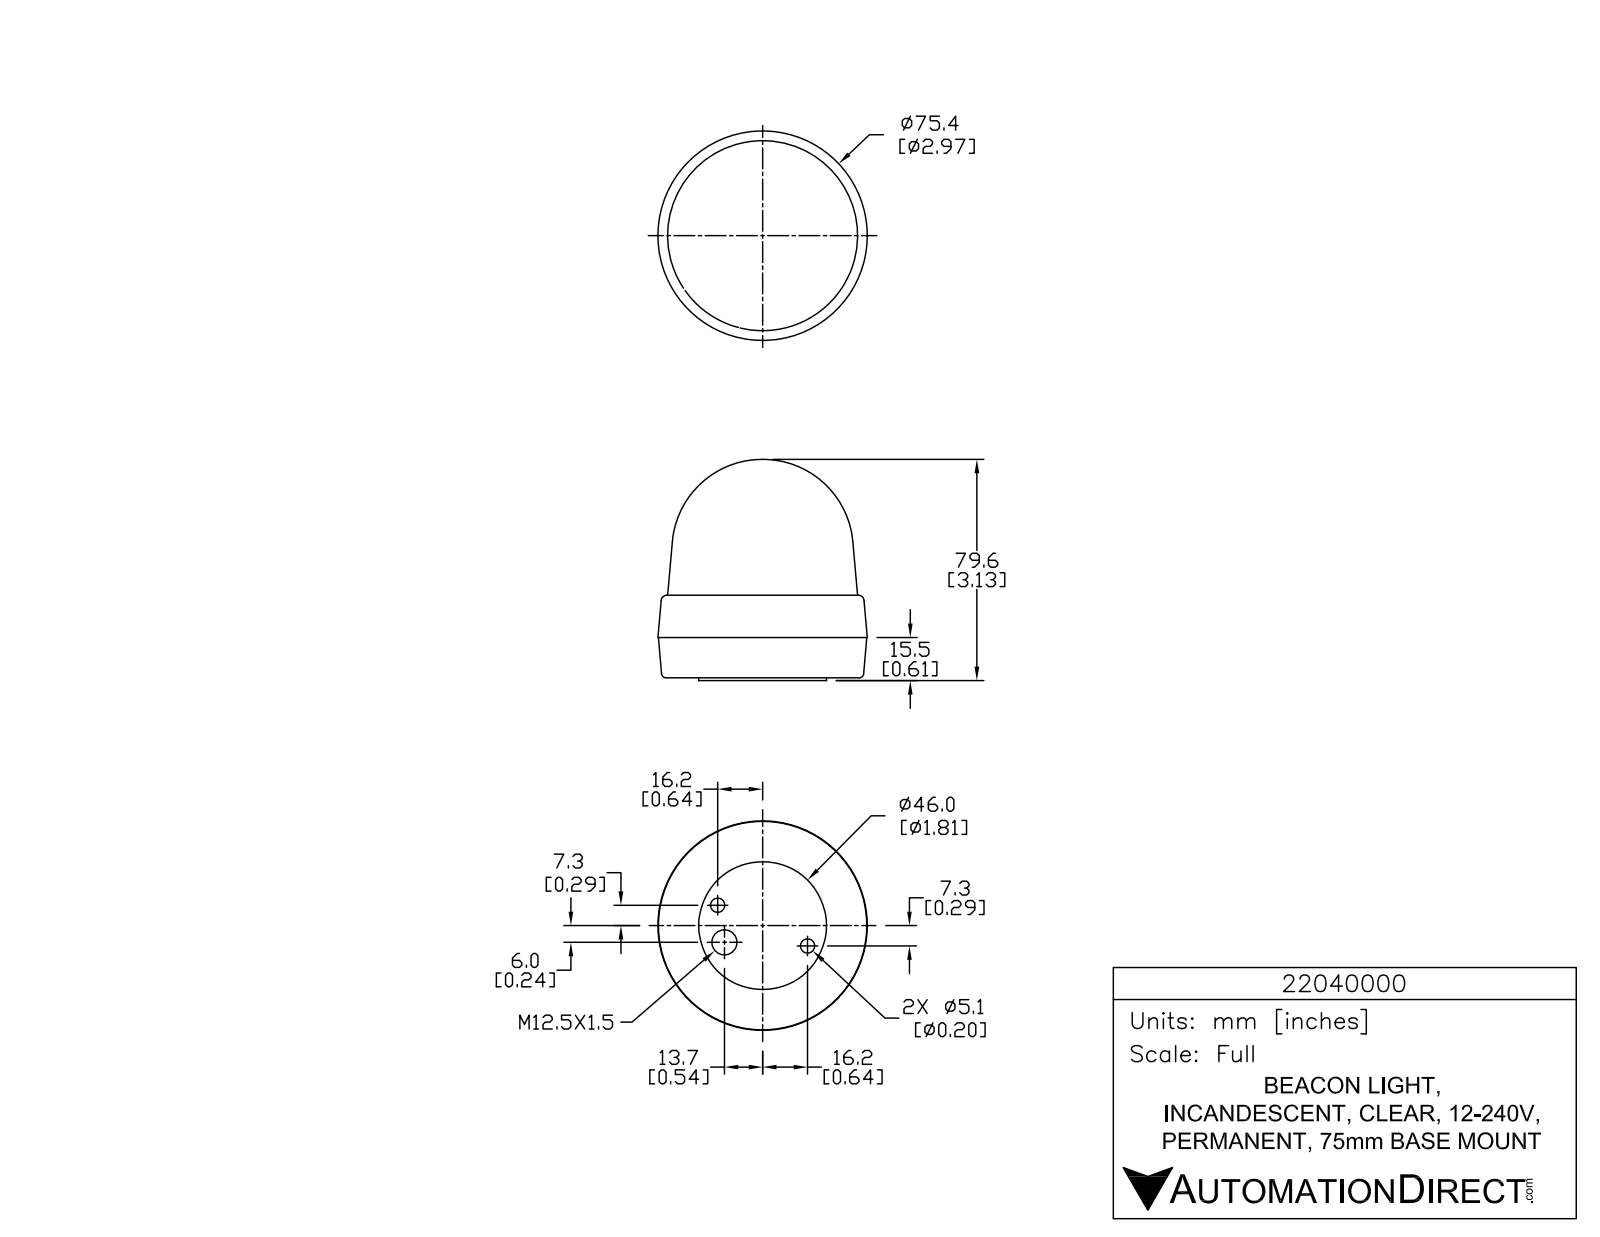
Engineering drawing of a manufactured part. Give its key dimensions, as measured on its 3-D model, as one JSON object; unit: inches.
{"part_name": "22040000", "step_written_by": "SolidWorks 2015 (AUTOMOTIVE_DESIGN)", "units": "inches", "bodies": {"solids": 1, "faces": 773, "planar": 526, "cylindrical": 163, "other": 84}, "overall_size": [3.133, 2.967, 2.967], "volume_in3": 15.79, "surface_area_in2": 33.7, "round_holes": [[0.059, 3], [0.201, 2], [0.354, 1]], "round_bosses_or_shafts": [[0.339, 3], [0.084, 3], [1.811, 1]], "partial_cylinders_radius": [[0.005, 9], [0.005, 6], [0.012, 6], [0.012, 6], [0.012, 6], [0.196, 6], [0.005, 3], [0.005, 3]], "face_to_face_distances": [0.039, 1.209, 1.17, 0.61, 0.571, 0.599, 1.566, 1.527, 0.956, 0.357], "hole_center_spacings": [0.534, 1.179, 1.398]}
